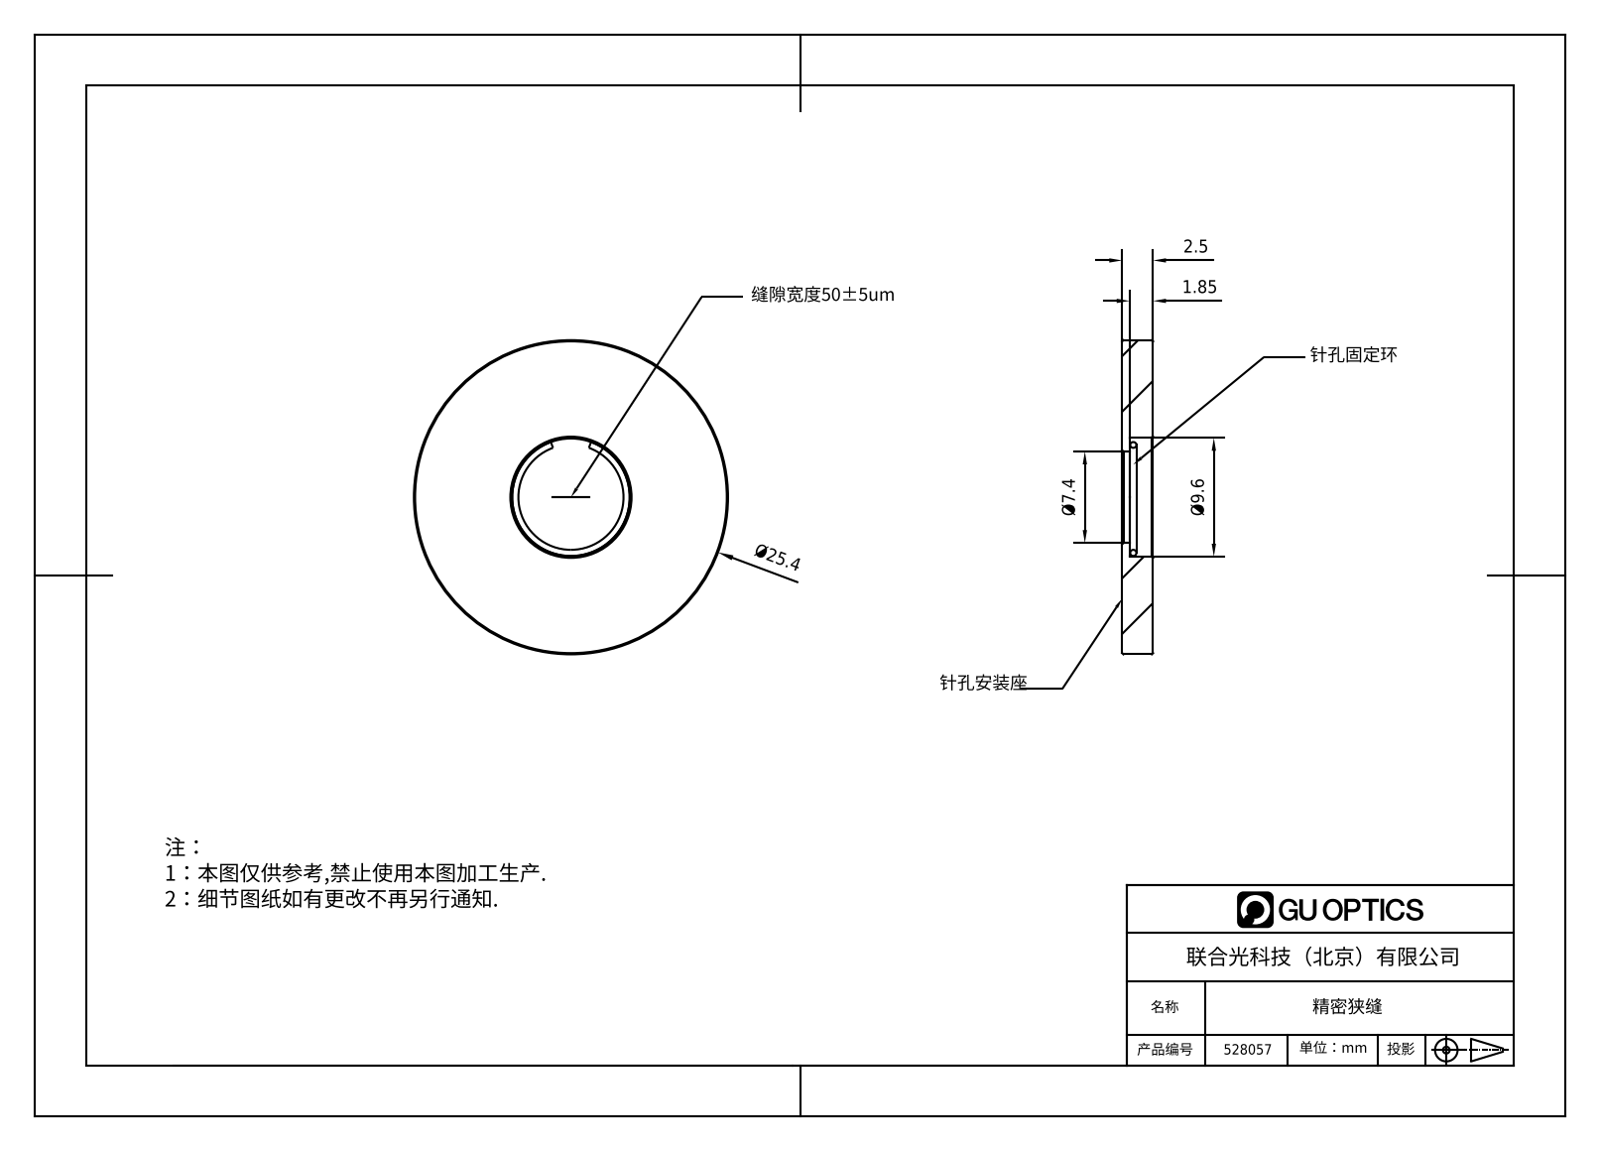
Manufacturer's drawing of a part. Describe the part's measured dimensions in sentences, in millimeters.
The part is named "528057". Its 3-D file was written by "SolidWorks 2020 (AUTOMOTIVE_DESIGN)". It is 2 solids with 33 faces: 11 planar, 8 cylindrical and 14 other. Overall it measures 25.4 by 25.4 by 2.5 millimeters. Its volume is 1 111 cubic millimeters and its surface area 1 313 square millimeters. Round holes: 1 of diameter 7.4, 1 of diameter 9.6. Round bosses or shafts: 1 of diameter 25.4, 1 of diameter 9.5. The main face-to-face distances are 2.5, 0.65, 1.85, 0.6, 1.9, 3.
